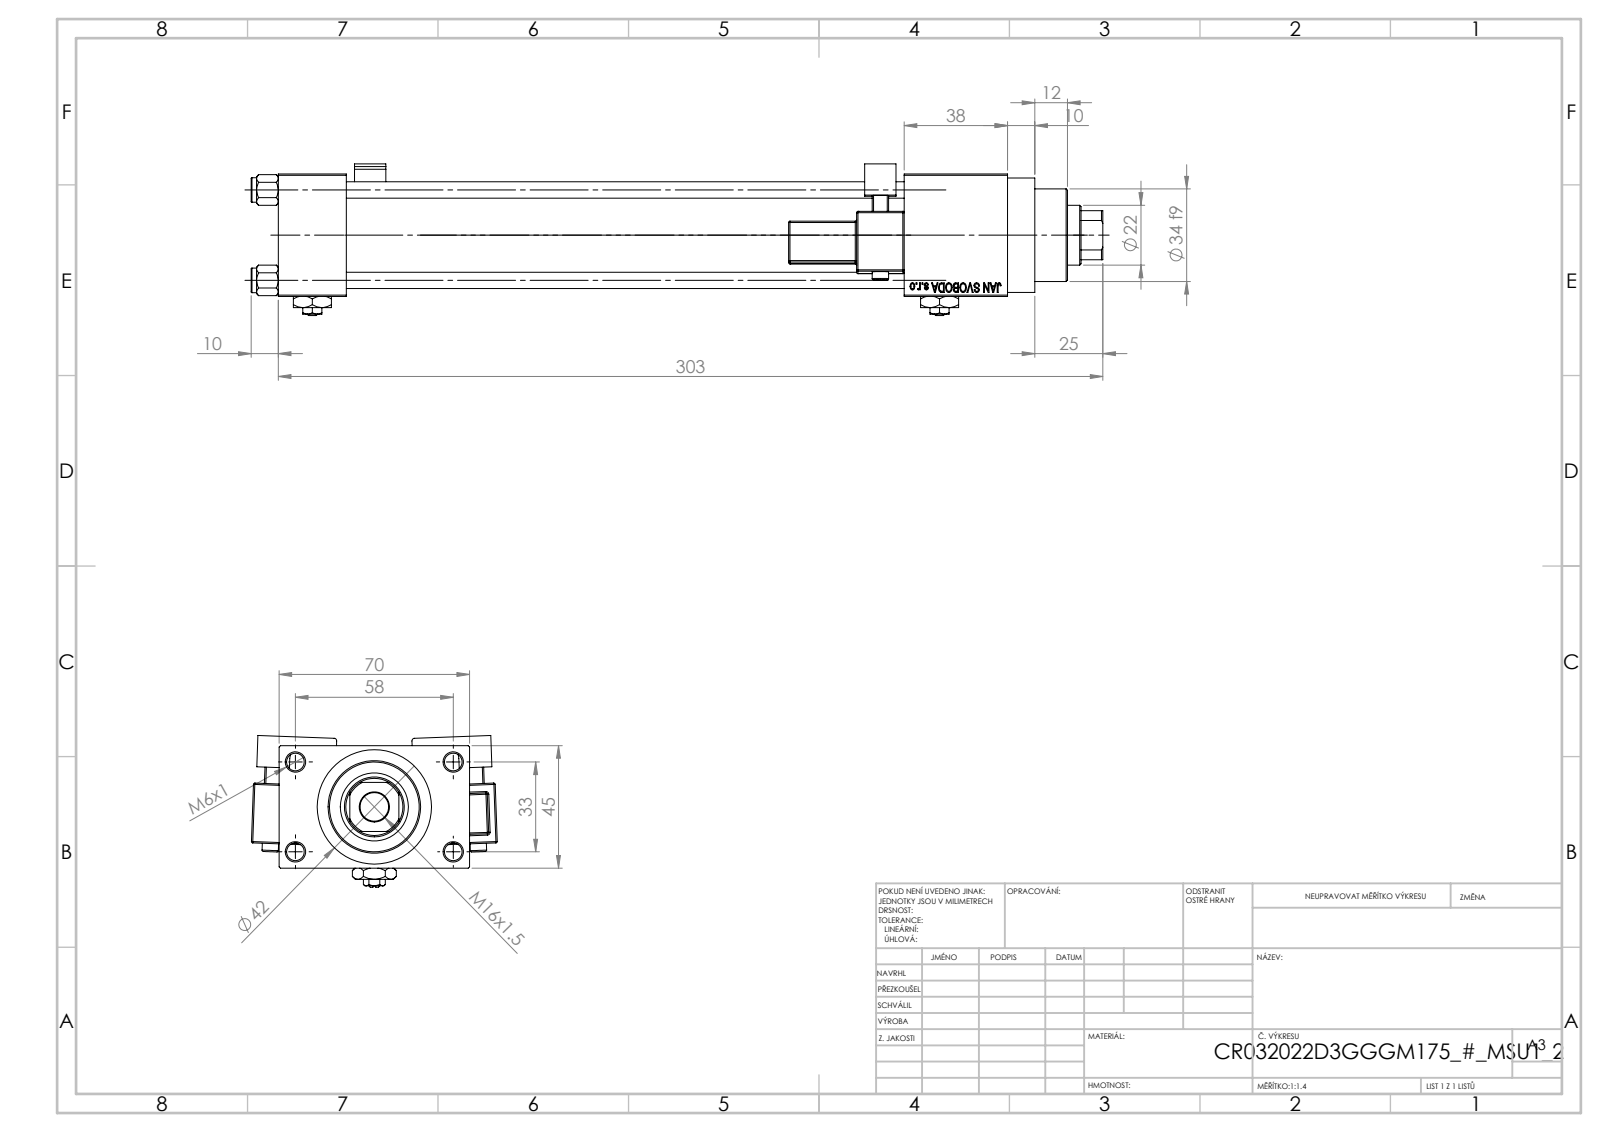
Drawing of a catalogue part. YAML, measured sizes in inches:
part_name: "V215CR_VCP_D; V215CR_D_Body; Zatka_pro_OIL_PORT; V215_VC_A (+3 more)"
step_written_by: "SolidWorks 2019 (CONFIG_CONTROL_DESIGN)"
units: inches
bodies: {solids: 15, faces: 1360, planar: 604, cylindrical: 160, other: 596}
overall_size: [12.323, 3.556, 2.194]
volume: 25.12
surface_area: 232
round_holes:
  - {diameter: 0.236, count: 4}
  - {diameter: 0.256, count: 4}
  - {diameter: 0.276, count: 2}
  - {diameter: 0.518, count: 2}
  - {diameter: 0.787, count: 2}
  - {diameter: 0.413, count: 1}
  - {diameter: 0.866, count: 1}
  - {diameter: 0.945, count: 1}
  - {diameter: 0.984, count: 1}
  - {diameter: 1.26, count: 1}
  - {diameter: 1.299, count: 1}
round_bosses_or_shafts:
  - {diameter: 0.354, count: 4}
  - {diameter: 0.236, count: 2}
  - {diameter: 1.654, count: 1}
  - {diameter: 1.496, count: 1}
  - {diameter: 1.339, count: 1}
partial_cylinders:
  - {radius: 0.02, count: 48}
  - {radius: 0.039, count: 2}
  - {radius: 0.098, count: 2}
  - {radius: 0.157, count: 2}
  - {radius: 0.413, count: 1}
face_to_face_distances: [1.772, 0.984, 0.492, 8.071, 0.118, 2.264, 9.055, 1.496, 9.567, 2.756]
hole_center_spacings: [0.488, 0.924, 1.307, 1.314, 1.392, 1.795, 2.219, 1.299]
